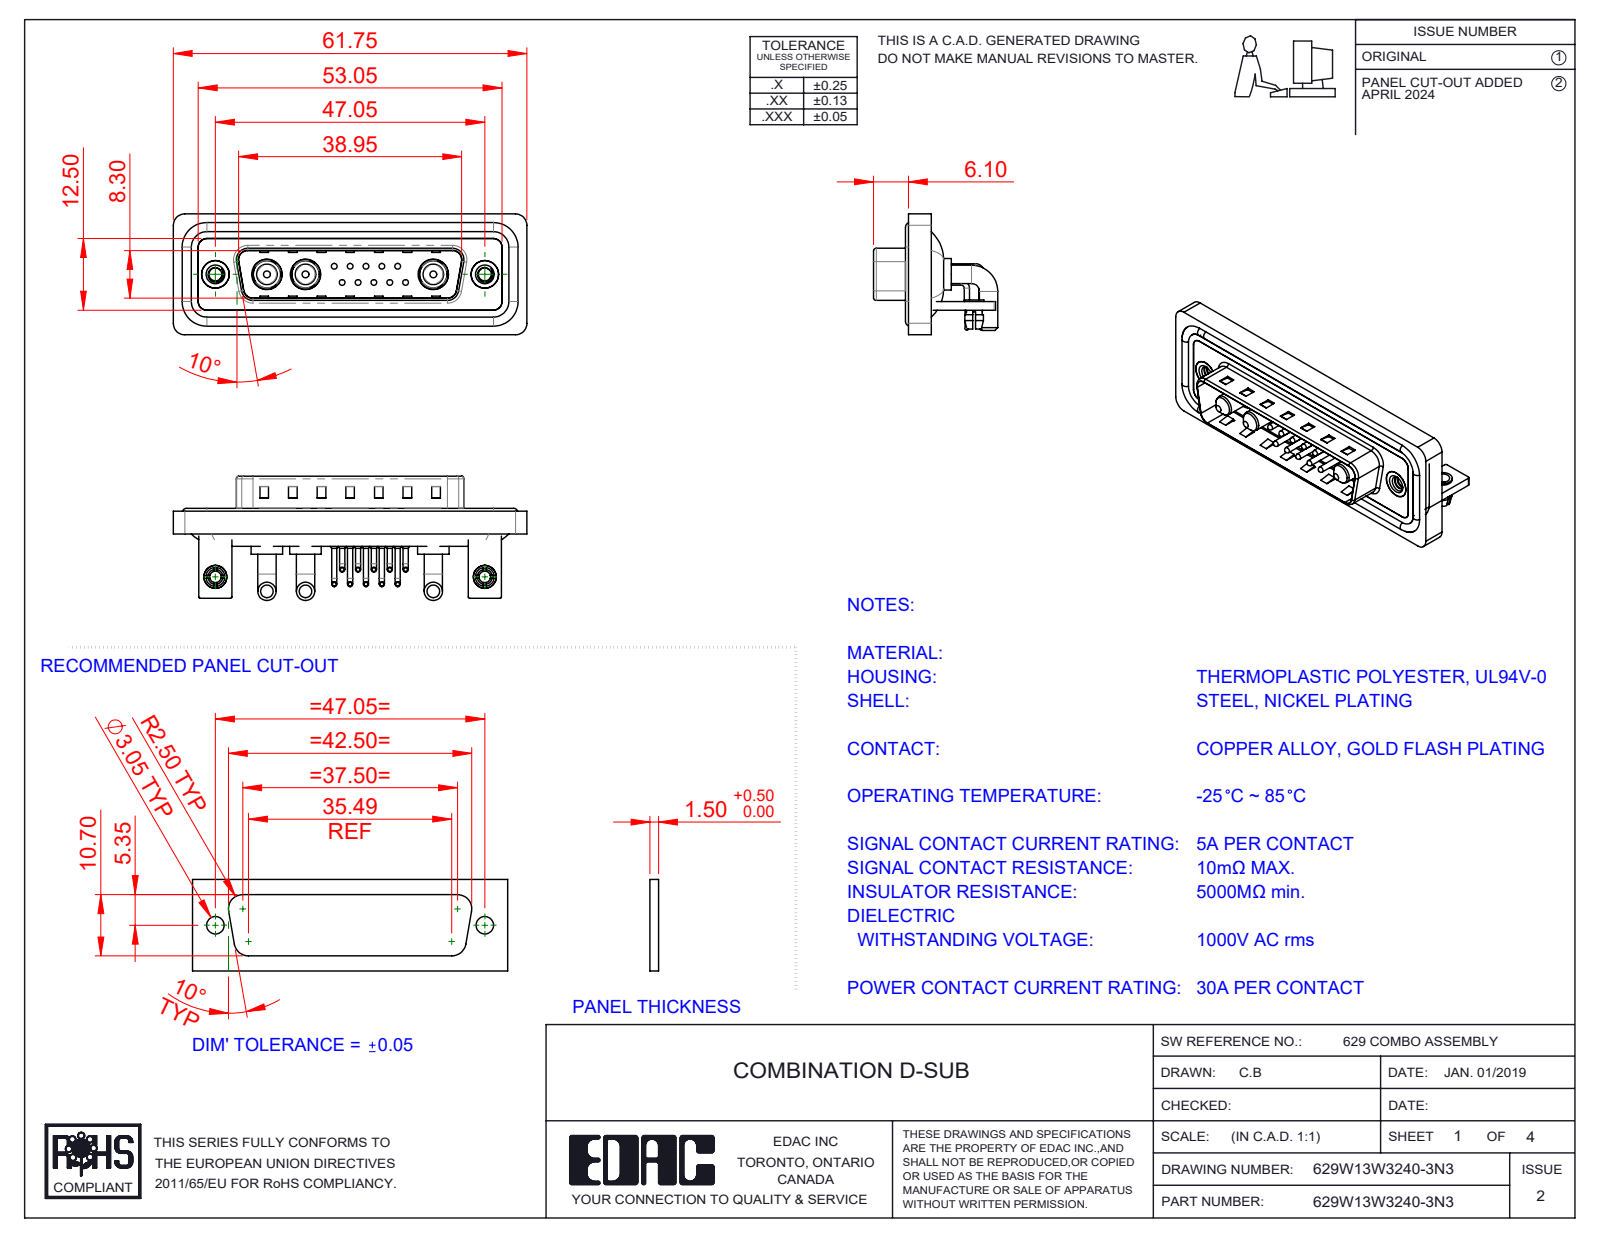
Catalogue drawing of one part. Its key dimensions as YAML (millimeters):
part_name: "629Combo Shell Rear_25 Contacts; 629Combo Housing_13W3; 629Combo Contact Row 1; 629Combo Shell Front_25 Contacts (+7 more)"
step_written_by: "SolidWorks 2023 (CONFIG_CONTROL_DESIGN)"
units: millimeters
bodies: {solids: 27, faces: 1844, planar: 947, cylindrical: 661, other: 236}
overall_size: [61.75, 21.7, 21.1]
volume: 8008
surface_area: 13349
round_holes:
  - {diameter: 2, count: 12}
  - {diameter: 0.75, count: 10}
  - {diameter: 1.6, count: 10}
  - {diameter: 4.85, count: 3}
  - {diameter: 5.3, count: 3}
  - {diameter: 2.26, count: 2}
  - {diameter: 2.5, count: 2}
  - {diameter: 3.2, count: 2}
  - {diameter: 4, count: 2}
  - {diameter: 4.8, count: 2}
  - {diameter: 5, count: 2}
round_bosses_or_shafts:
  - {diameter: 0.9, count: 20}
  - {diameter: 1.5, count: 10}
  - {diameter: 1, count: 10}
  - {diameter: 0.65, count: 10}
  - {diameter: 3.2, count: 6}
  - {diameter: 1.6, count: 4}
  - {diameter: 5.5, count: 3}
  - {diameter: 5.2, count: 3}
partial_cylinders:
  - {radius: 2, count: 19}
  - {radius: 1.5, count: 18}
  - {radius: 0.25, count: 16}
  - {radius: 1.01, count: 10}
  - {radius: 0.5, count: 9}
  - {radius: 1.6, count: 8}
  - {radius: 0.6, count: 4}
  - {radius: 0.65, count: 4}
face_to_face_distances: [0.4, 0.8, 1.5, 2.9, 2.1, 1.1, 4.1, 1.6, 3.7, 4.5]
hole_center_spacings: [3.16, 2.77, 5.04, 5.54, 7.49, 5.03, 8.31, 10.11]
